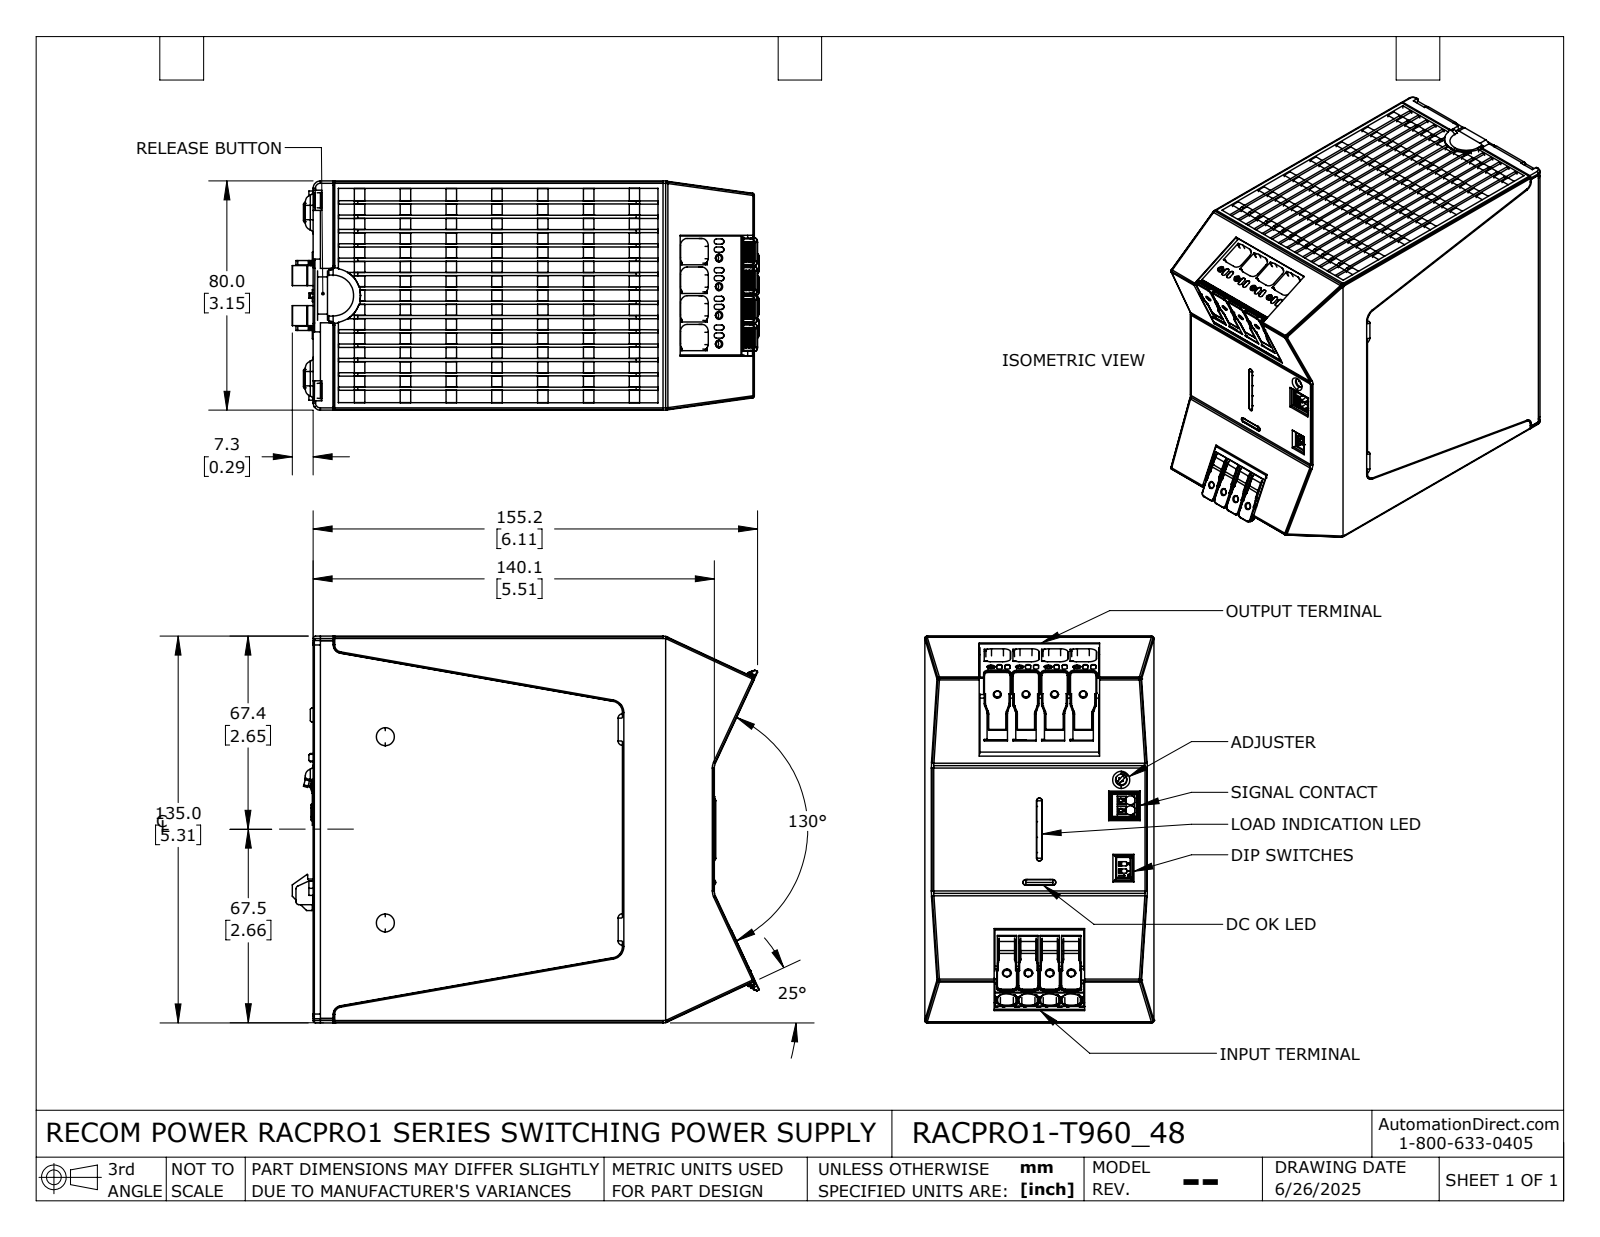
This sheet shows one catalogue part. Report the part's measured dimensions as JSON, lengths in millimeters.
{"part_name": "RACPRO1-T960_48", "step_written_by": "SolidWorks 2024 (AUTOMOTIVE_DESIGN)", "units": "millimeters", "bodies": {"solids": 1, "faces": 4784, "planar": 2279, "cylindrical": 1514, "other": 991}, "overall_size": [163, 135, 80], "volume_mm3": 1518000, "surface_area_mm2": 120500, "round_holes": [[2.2, 8], [2, 4], [2.5, 4], [1, 2], [1.5, 2], [1.6, 2], [1.9, 2], [1.5, 1], [1.7, 1], [4, 1], [5.3, 1]], "round_bosses_or_shafts": [[5, 2], [1.9, 2], [1.5, 2], [3.8, 1]], "partial_cylinders_radius": [[0.2, 226], [0.3, 138], [0.3, 56], [3, 48], [1, 46], [0.5, 44], [2.5, 31], [0.8, 24]], "face_to_face_distances": [80, 1.5, 78.5, 133.3, 0.5, 134.5, 5, 140.1, 10, 14.9], "hole_center_spacings": [10, 20, 7.5, 15, 30, 6.5, 10.2, 10.6]}
